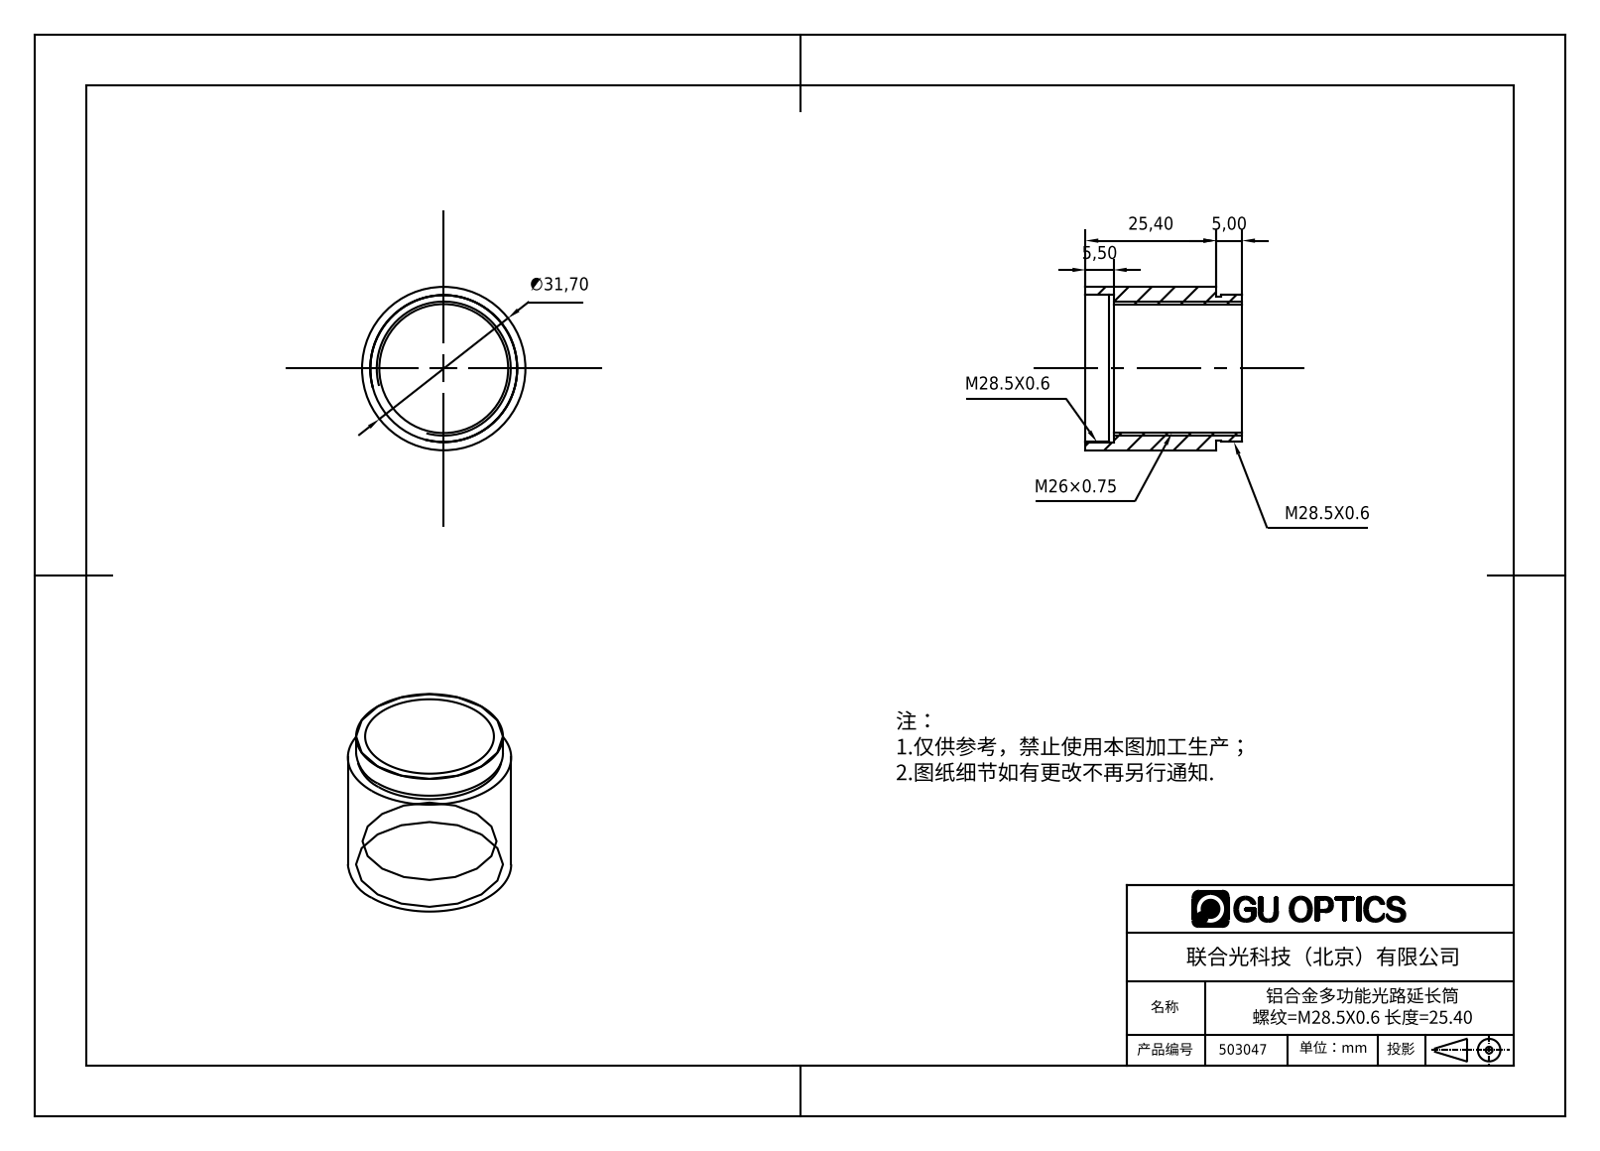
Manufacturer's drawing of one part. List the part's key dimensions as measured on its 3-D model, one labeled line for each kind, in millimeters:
Part name (STEP PRODUCT): 503047
STEP written by: SolidWorks 2016 (AUTOMOTIVE_DESIGN)
Units: millimetres
Bodies: 1 solid, 18 faces (6 planar, 12 cylindrical, 0 other)
Overall size (bounding box): 31.7 × 31.7 × 30.4
Volume: 7 474 mm³ · Surface area: 6 083 mm²
Round holes (diameter × count): ⌀25 ×1, ⌀28.5 ×1, ⌀28.7 ×1
Round bosses / shafts (diameter × count): ⌀31.7 ×1, ⌀28 ×1
Main face-to-face distances: 19.9, 5.5, 25.4, 30.4, 24.9, 5, 1, 20.9, 26.4, 4
